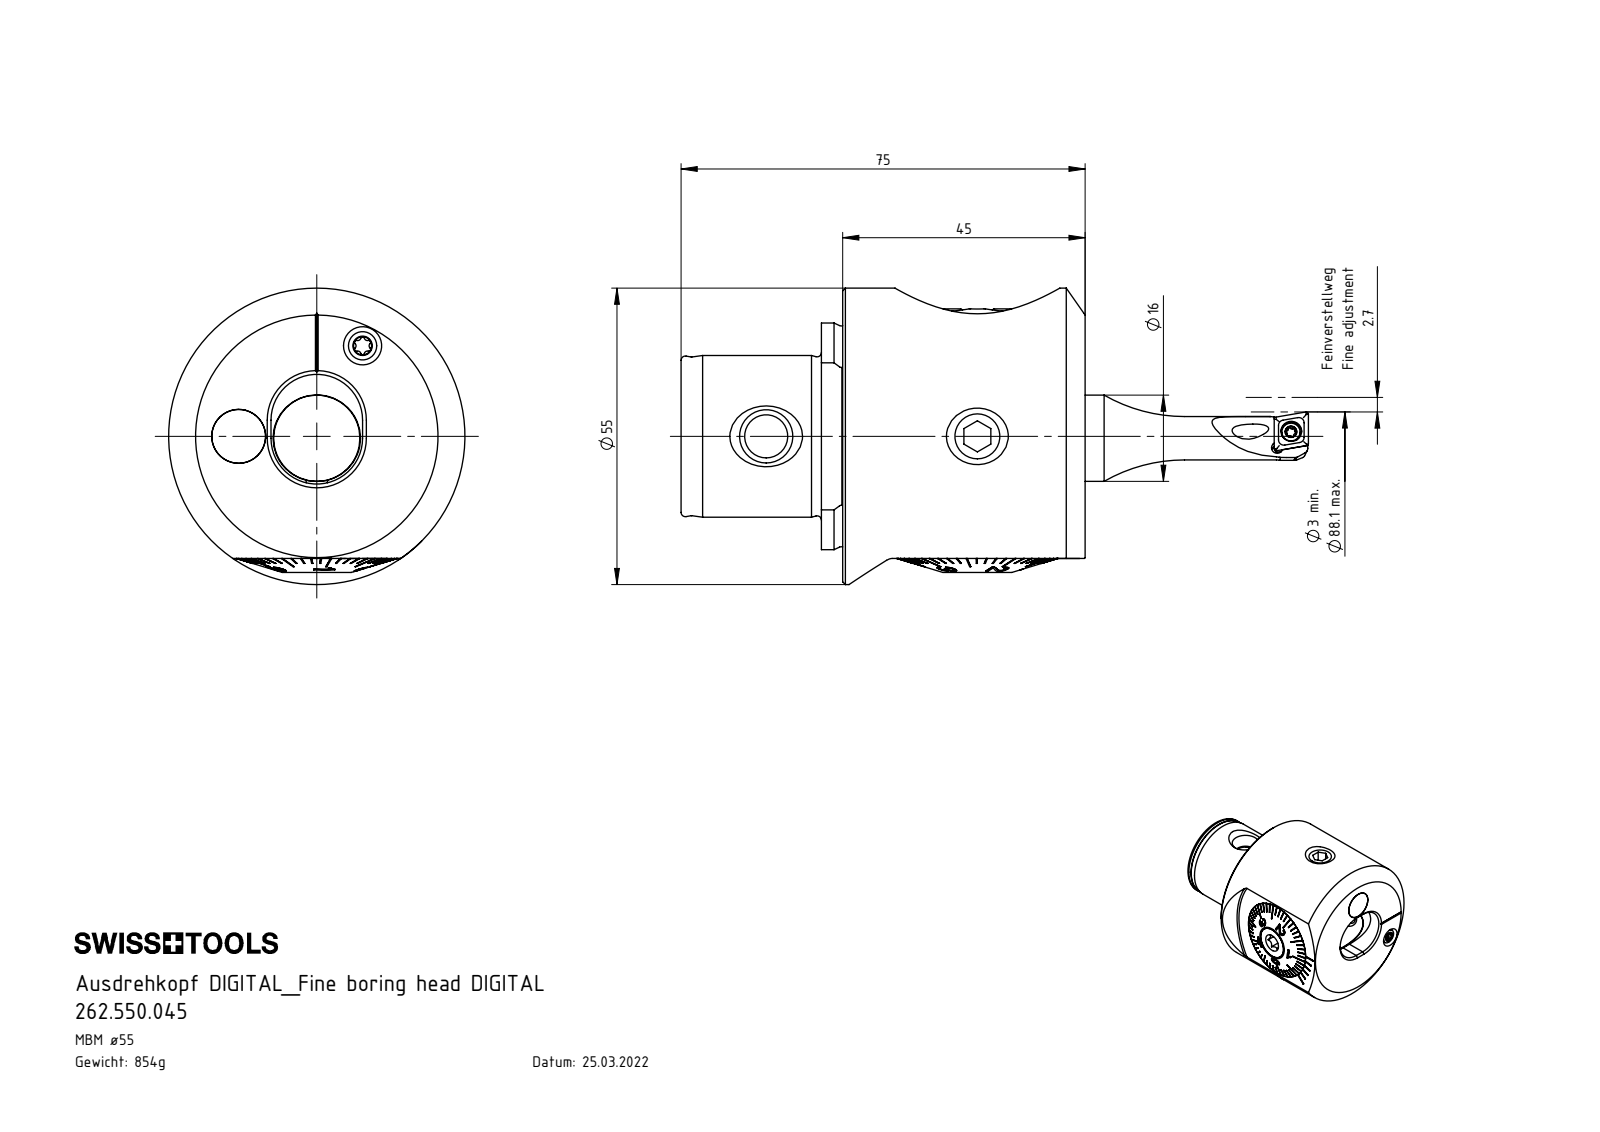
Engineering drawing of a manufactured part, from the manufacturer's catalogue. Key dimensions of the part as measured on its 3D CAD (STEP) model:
Part name (STEP PRODUCT): A55-BG3.011.033_A_gekrzt; MB5.A55.AA4.045; ISO 4026 - M10 x 16_PreviewCfg; A55-BG1.012.007_C (+8 more)
STEP written by: SolidWorks 2017 (AUTOMOTIVE_DESIGN)
Units: millimetres
Bodies: 14 solids, 580 faces (318 planar, 79 cylindrical, 183 other)
Overall size (bounding box): 75 × 55 × 55
Volume: 97 739 mm³ · Surface area: 37 322 mm²
Round holes (diameter × count): ⌀8.5 ×3, ⌀8 ×2, ⌀1.6 ×1, ⌀3.3 ×1, ⌀4.2 ×1, ⌀10 ×1, ⌀11.4 ×1, ⌀12.4 ×1, ⌀14 ×1, ⌀14.2 ×1, ⌀16 ×1, ⌀20 ×1
Round bosses / shafts (diameter × count): ⌀10 ×3, ⌀30 ×2, ⌀55 ×1, ⌀29.98 ×1, ⌀29.9 ×1, ⌀25 ×1, ⌀18 ×1, ⌀12 ×1
Partial cylindrical surfaces — rounded edges, fillets, slot ends (radius × count): R0.34 ×6, R0.59 ×6, R1.4 ×4, R1.9 ×4, R3.2 ×3, R2 ×2, R8.5 ×2, R1 ×1
Main face-to-face distances: 45, 5.3, 2.8, 2.5, 6.5, 3.7, 1.2, 3.95, 48.95, 2.7
Hole centre spacings: 7.25, 14.5, 19.14, 28.48, 39.2
